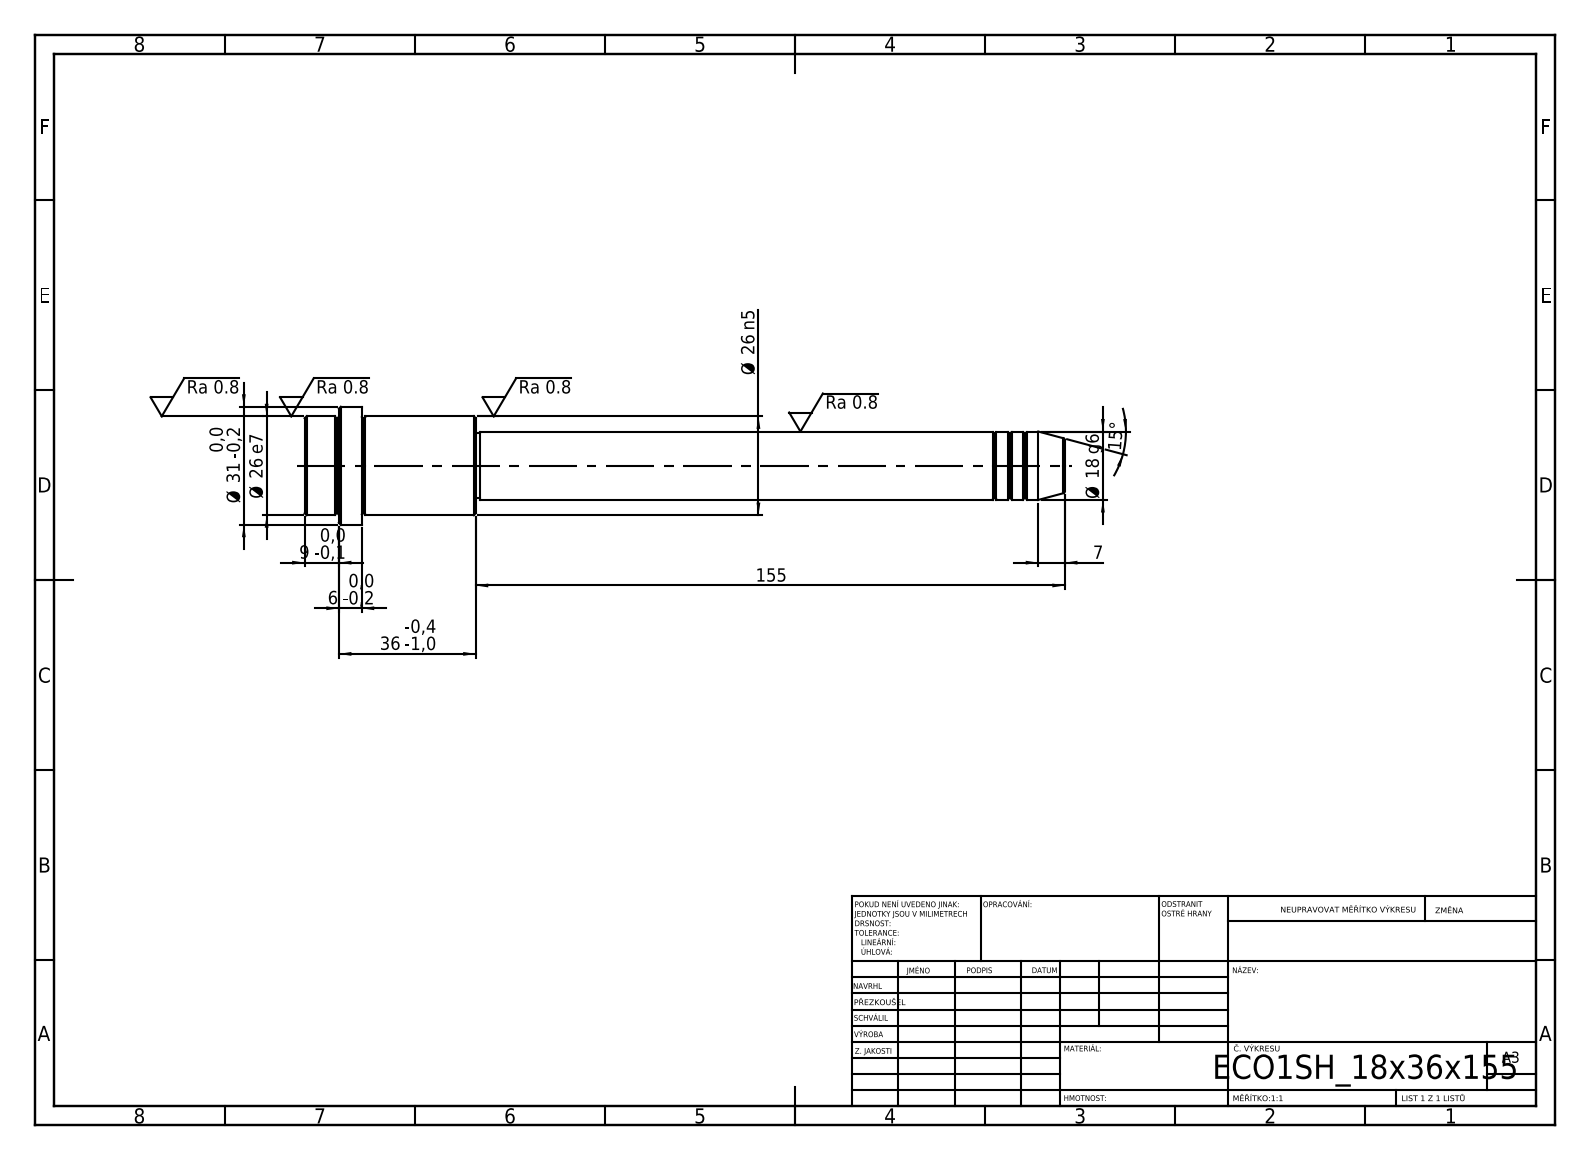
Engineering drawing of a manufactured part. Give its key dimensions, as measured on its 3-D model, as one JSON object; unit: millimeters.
{"step_written_by": "SolidWorks 2019 (CONFIG_CONTROL_DESIGN)", "units": "millimeters", "bodies": {"solids": 1, "faces": 52, "planar": 6, "cylindrical": 16, "other": 30}, "overall_size": [200, 31, 31], "volume_mm3": 64143, "surface_area_mm2": 14064, "round_bosses_or_shafts": [[31, 1], [26, 1], [18, 1], [17, 1]], "face_to_face_distances": [45, 30, 15, 36, 6, 9, 155, 185, 191, 200]}
